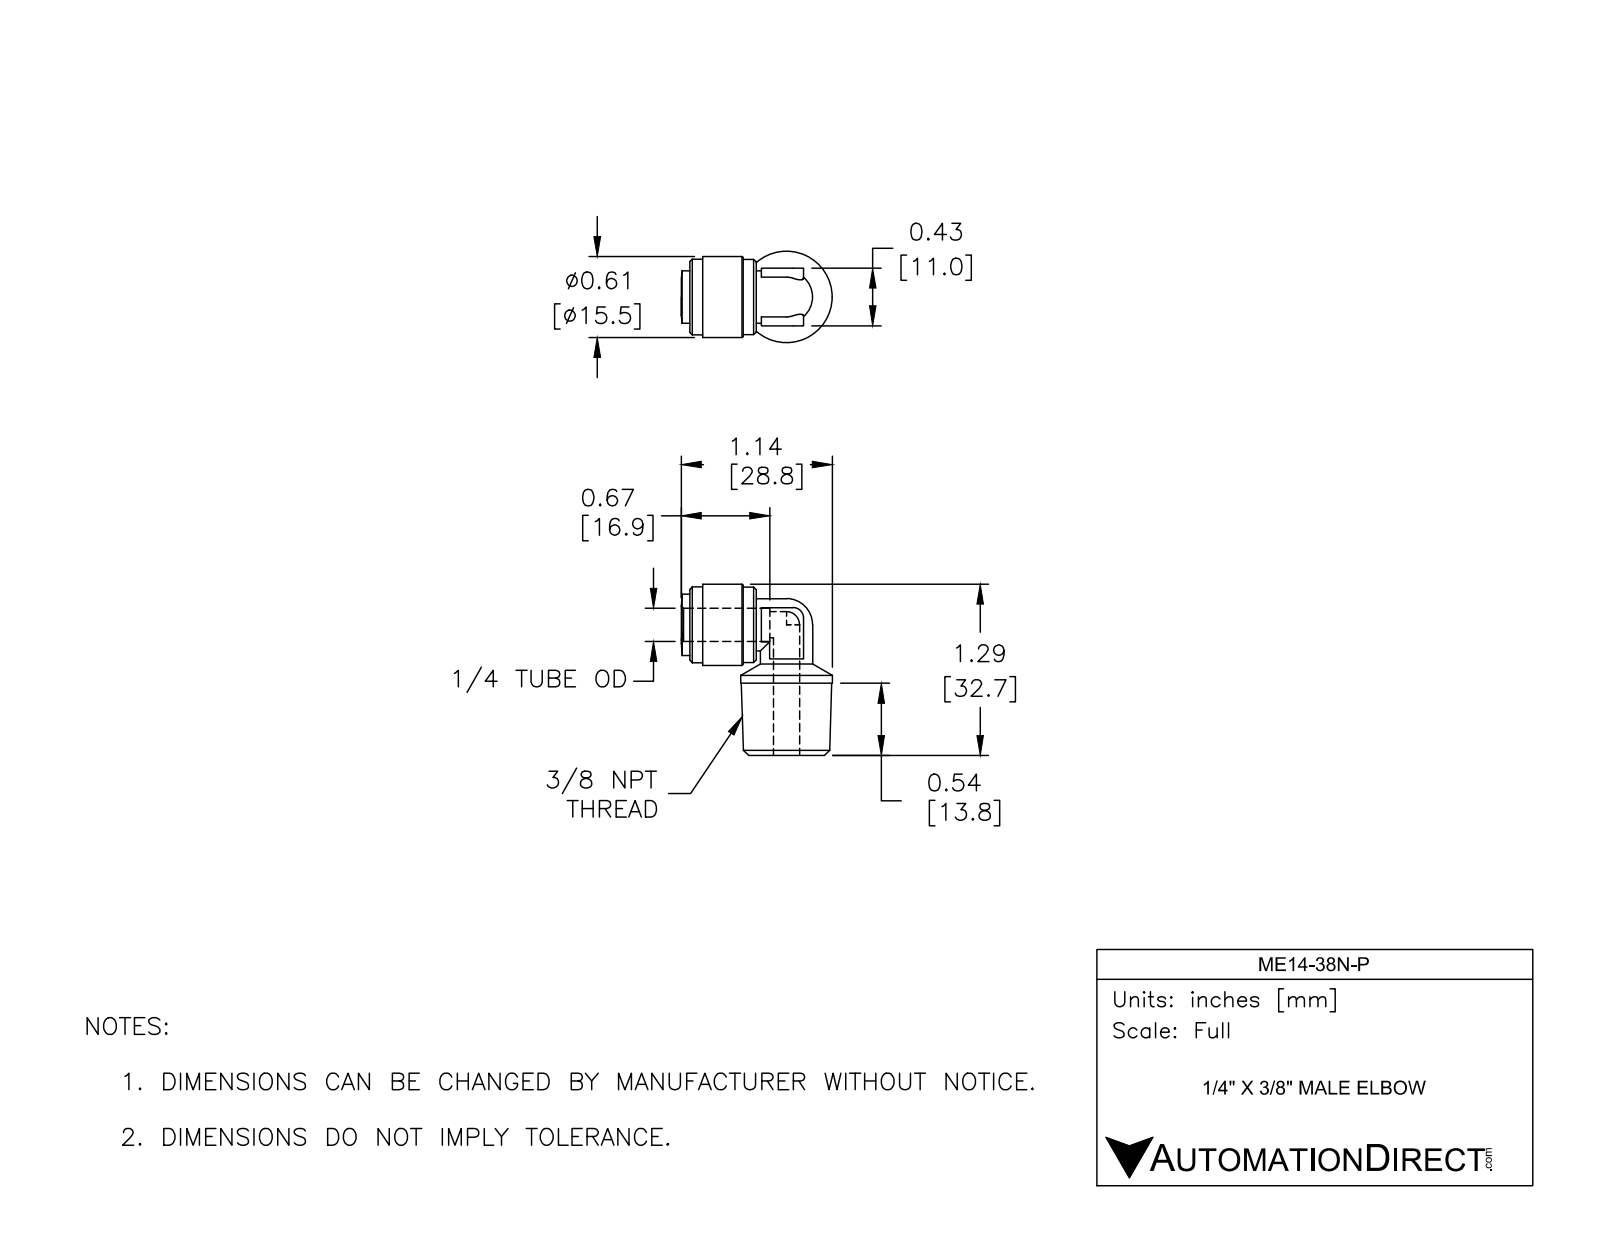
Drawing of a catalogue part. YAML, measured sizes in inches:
part_name: "ME14-38N-P"
step_written_by: "SolidWorks 2017 (AUTOMOTIVE_DESIGN)"
units: inches
bodies: {solids: 1, faces: 63, planar: 21, cylindrical: 20, other: 22}
overall_size: [1.288, 1.136, 0.689]
volume: 0.379
surface_area: 5.147
round_holes:
  - {diameter: 0.197, count: 2}
  - {diameter: 0.25, count: 1}
round_bosses_or_shafts:
  - {diameter: 0.394, count: 2}
  - {diameter: 0.689, count: 1}
  - {diameter: 0.61, count: 1}
  - {diameter: 0.571, count: 1}
  - {diameter: 0.567, count: 1}
partial_cylinders:
  - {radius: 0.079, count: 1}
face_to_face_distances: [0.433, 0.5, 0.098, 0.402, 0.856, 0.356, 0.758, 1.111, 0.256, 0.303]
